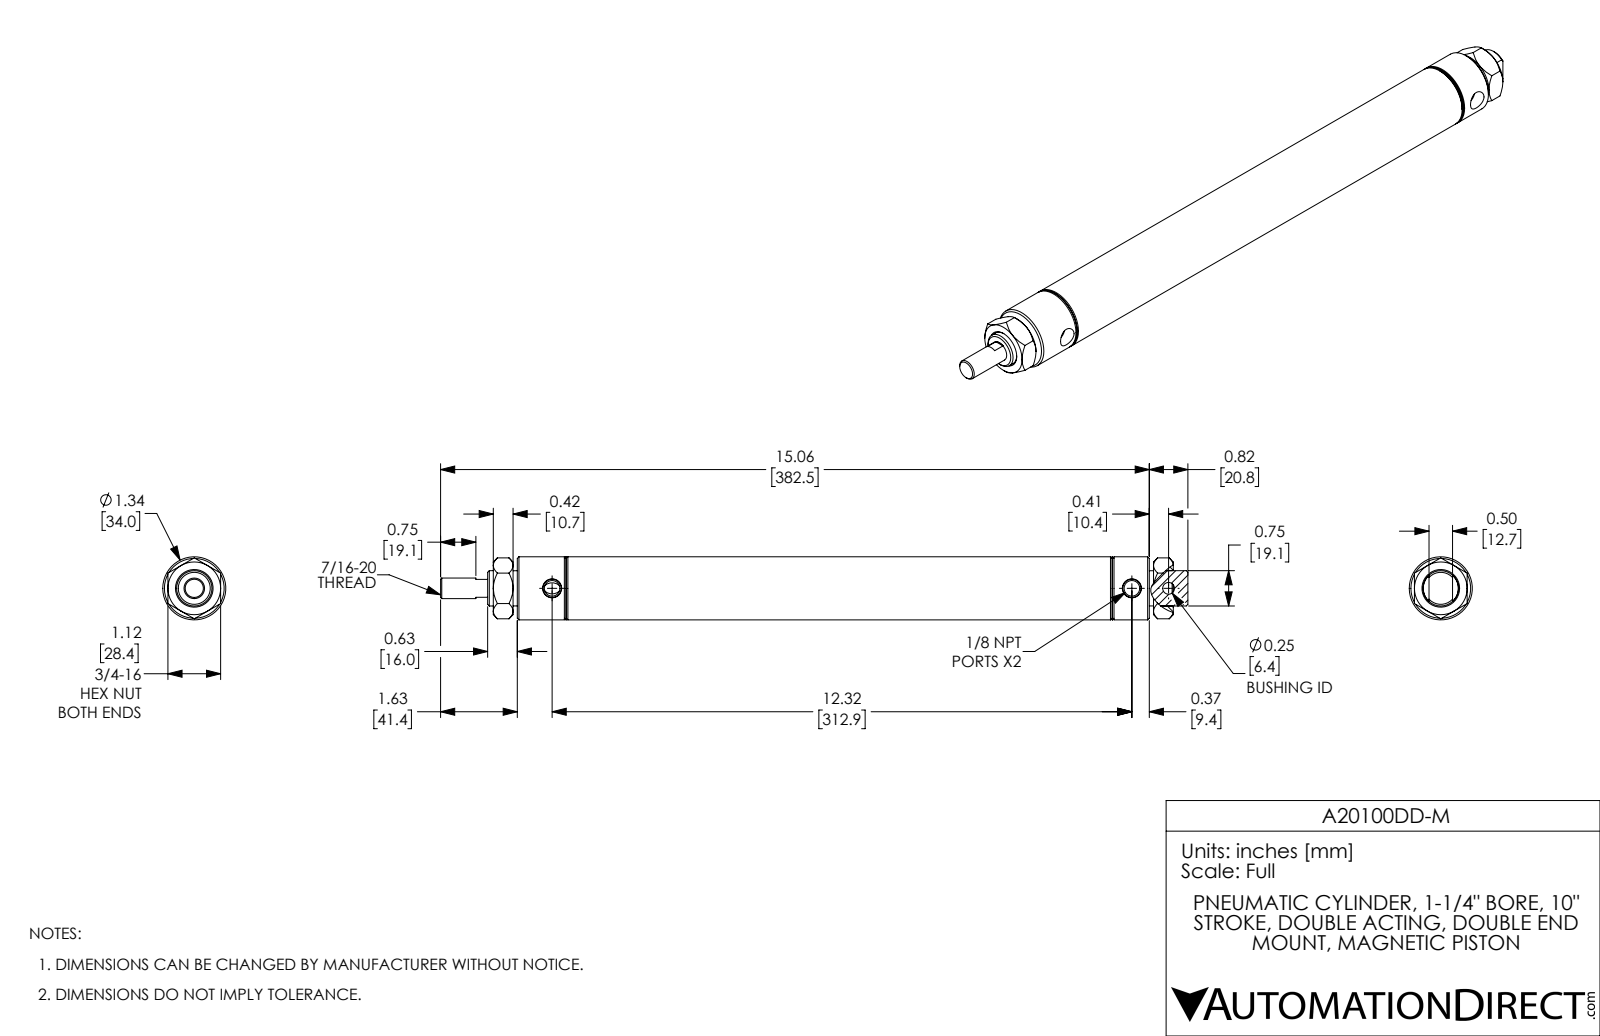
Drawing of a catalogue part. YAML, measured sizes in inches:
part_name: "A20100DD-M-Rod; A20100DD-M-MainBody; A20100DD-M; A20100DD-M_Mounting Nut_D-3556"
step_written_by: "SolidWorks 2017 (AUTOMOTIVE_DESIGN)"
units: inches
bodies: {solids: 4, faces: 138, planar: 44, cylindrical: 36, other: 58}
overall_size: [15.88, 1.34, 1.34]
volume: 9.27
surface_area: 140.4
round_holes:
  - {diameter: 0.332, count: 2}
  - {diameter: 0.251, count: 1}
  - {diameter: 0.437, count: 1}
  - {diameter: 0.75, count: 1}
  - {diameter: 1.25, count: 1}
round_bosses_or_shafts:
  - {diameter: 1.34, count: 1}
  - {diameter: 0.747, count: 1}
face_to_face_distances: [1.465, 11.965, 0.5, 1.12, 10.5, 10, 0.31, 0.42, 14.03, 1.965]
hole_center_spacings: [0.78, 12.32, 13.1]
